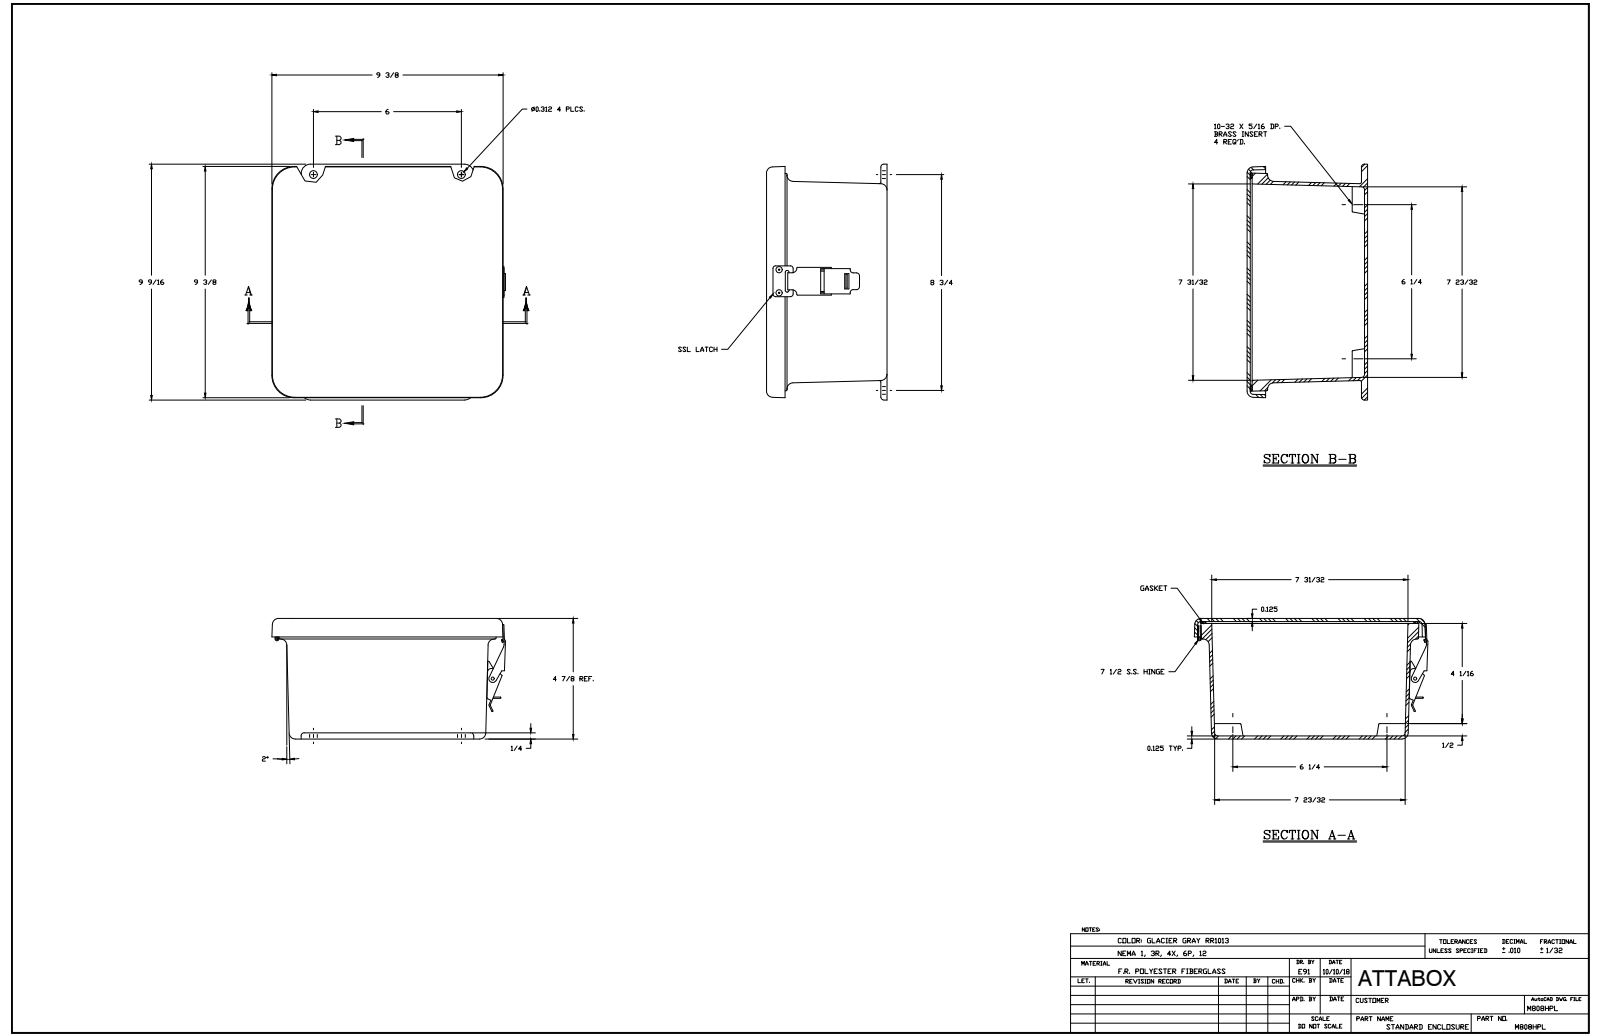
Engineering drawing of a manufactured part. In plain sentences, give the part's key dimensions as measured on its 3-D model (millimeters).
The part is named "M808HPL". Its 3-D file was written by "SolidWorks 2018 (AUTOMOTIVE_DESIGN)". It is 26 solids with 779 faces: 293 planar, 313 cylindrical and 173 other. Overall it measures 242.9 by 242.1 by 124.2 millimeters. Its volume is 848 700 cubic millimeters and its surface area 484 600 square millimeters. Round holes: 12 of diameter 3.6, 8 of diameter 3.9, 6 of diameter 3.3, 4 of diameter 2.6, 4 of diameter 4, 4 of diameter 5.5, 2 of diameter 3.3, 2 of diameter 3.4, 1 of diameter 2.2, 1 of diameter 9.5. Round bosses or shafts: 8 of diameter 3.2, 6 of diameter 6.4, 4 of diameter 6.9, 2 of diameter 3.2, 1 of diameter 7.6, 1 of diameter 4.3, 1 of diameter 3.9, 1 of diameter 3.4. Partial cylindrical surfaces (rounded edges, fillets, slot ends): 36 of radius 0.8, 16 of radius 3.2, 12 of radius 0.4, 12 of radius 6.4, 8 of radius 1.1, 7 of radius 5.1, 6 of radius 0.8, 5 of radius 0.6. The main face-to-face distances are 3.2, 121, 124.2, 117.8, 3.2, 121, 115.8, 5.2, 2, 119. The hole center spacings are 88.9, 184.1, 23.8, 206.4, 258.2, 6.4, 19.1, 82.6.
